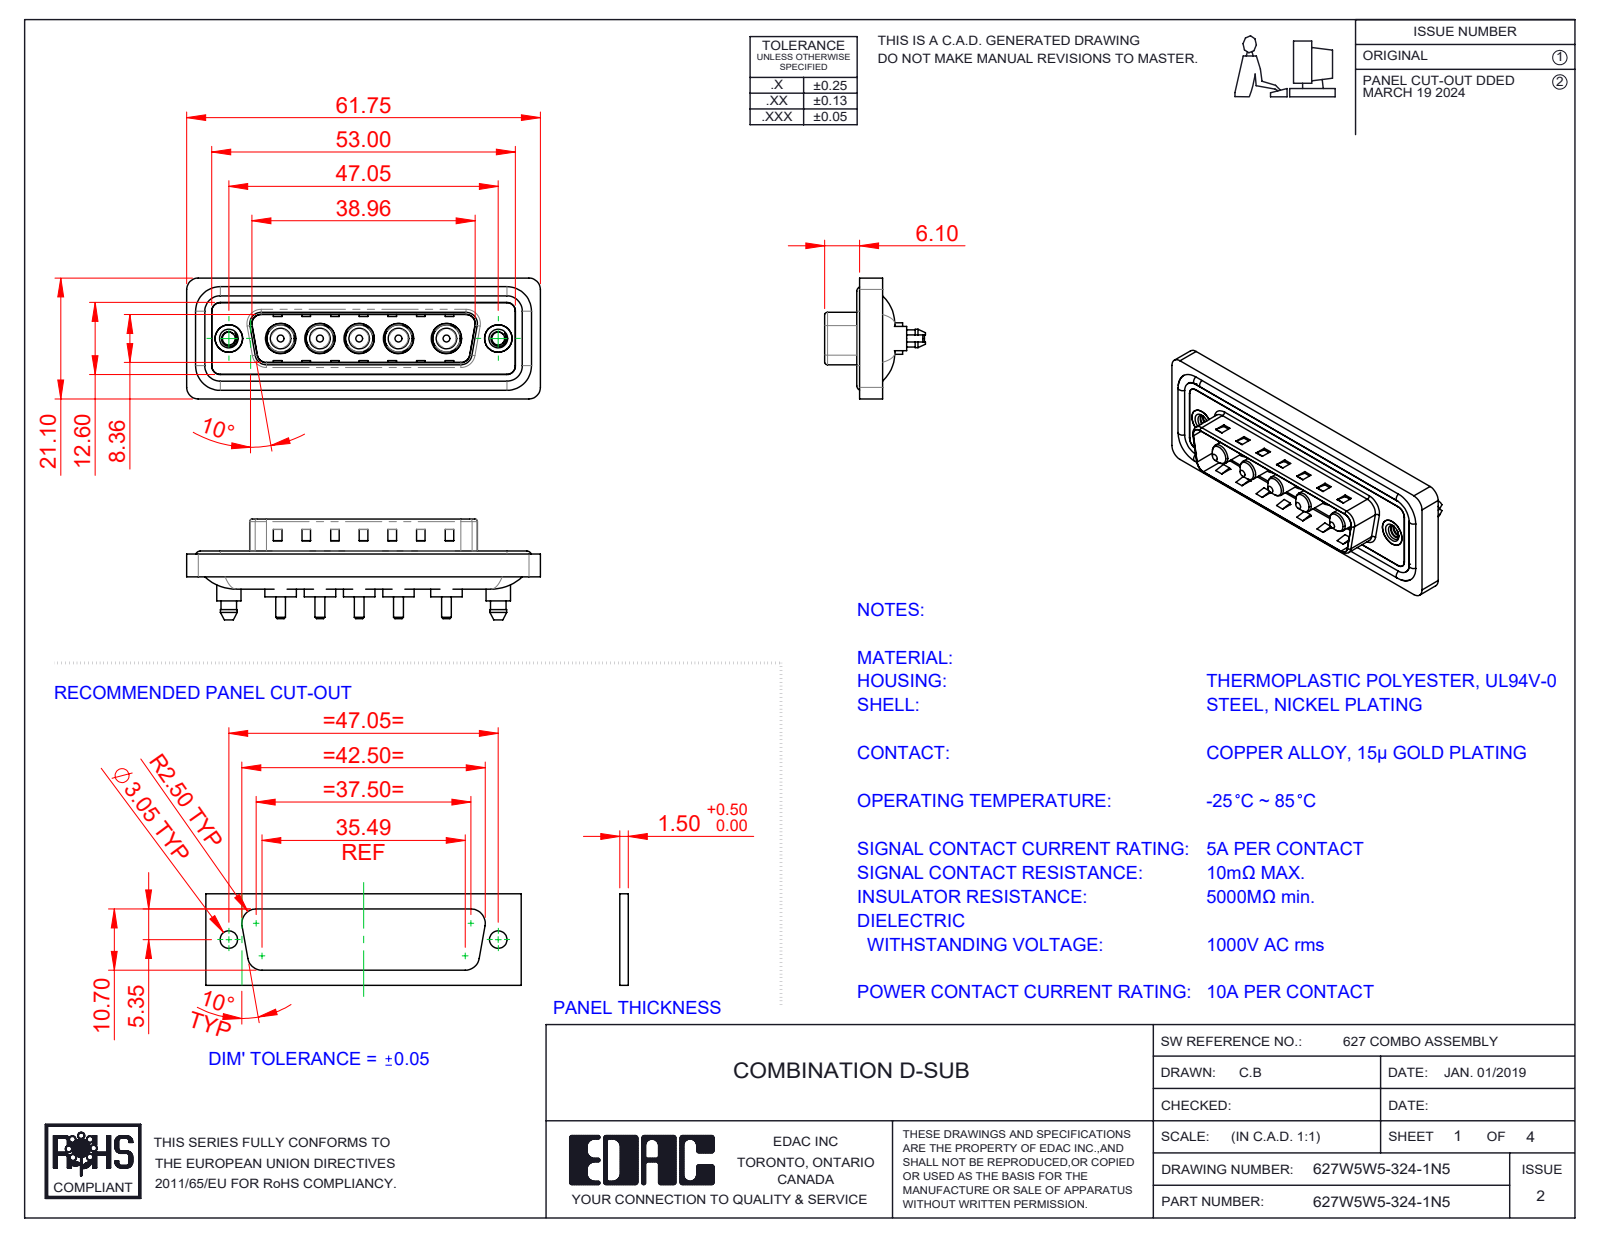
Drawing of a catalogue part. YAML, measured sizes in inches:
part_name: "627Combo Threaded Boardlock_5; 627Combo Shell Rear_25 Contacts; 627W5W5-324-1N5; 627Combo Shell Front_25 Contacts (+3 more)"
step_written_by: "SolidWorks 2023 (CONFIG_CONTROL_DESIGN)"
units: inches
bodies: {solids: 17, faces: 728, planar: 275, cylindrical: 315, other: 138}
overall_size: [2.431, 0.831, 0.693]
volume: 0.46
surface_area: 18.7
round_holes:
  - {diameter: 0.191, count: 5}
  - {diameter: 0.209, count: 5}
  - {diameter: 0.089, count: 2}
  - {diameter: 0.157, count: 2}
  - {diameter: 0.189, count: 2}
  - {diameter: 0.197, count: 2}
round_bosses_or_shafts:
  - {diameter: 0.217, count: 5}
  - {diameter: 0.205, count: 5}
  - {diameter: 0.187, count: 5}
  - {diameter: 0.148, count: 5}
  - {diameter: 0.142, count: 5}
  - {diameter: 0.067, count: 5}
  - {diameter: 0.063, count: 4}
  - {diameter: 0.213, count: 2}
partial_cylinders:
  - {radius: 0.059, count: 24}
  - {radius: 0.079, count: 18}
  - {radius: 0.063, count: 10}
  - {radius: 0.02, count: 8}
  - {radius: 0.083, count: 5}
  - {radius: 0.01, count: 4}
  - {radius: 0.024, count: 4}
  - {radius: 0.026, count: 4}
face_to_face_distances: [0.016, 0.059, 0.043, 0.02, 0.122, 0.063, 0.114, 0.032, 0.377, 0.222]
hole_center_spacings: [0.27, 0.356, 0.541, 1.496, 0.27, 0.33, 0.33, 0.356]
